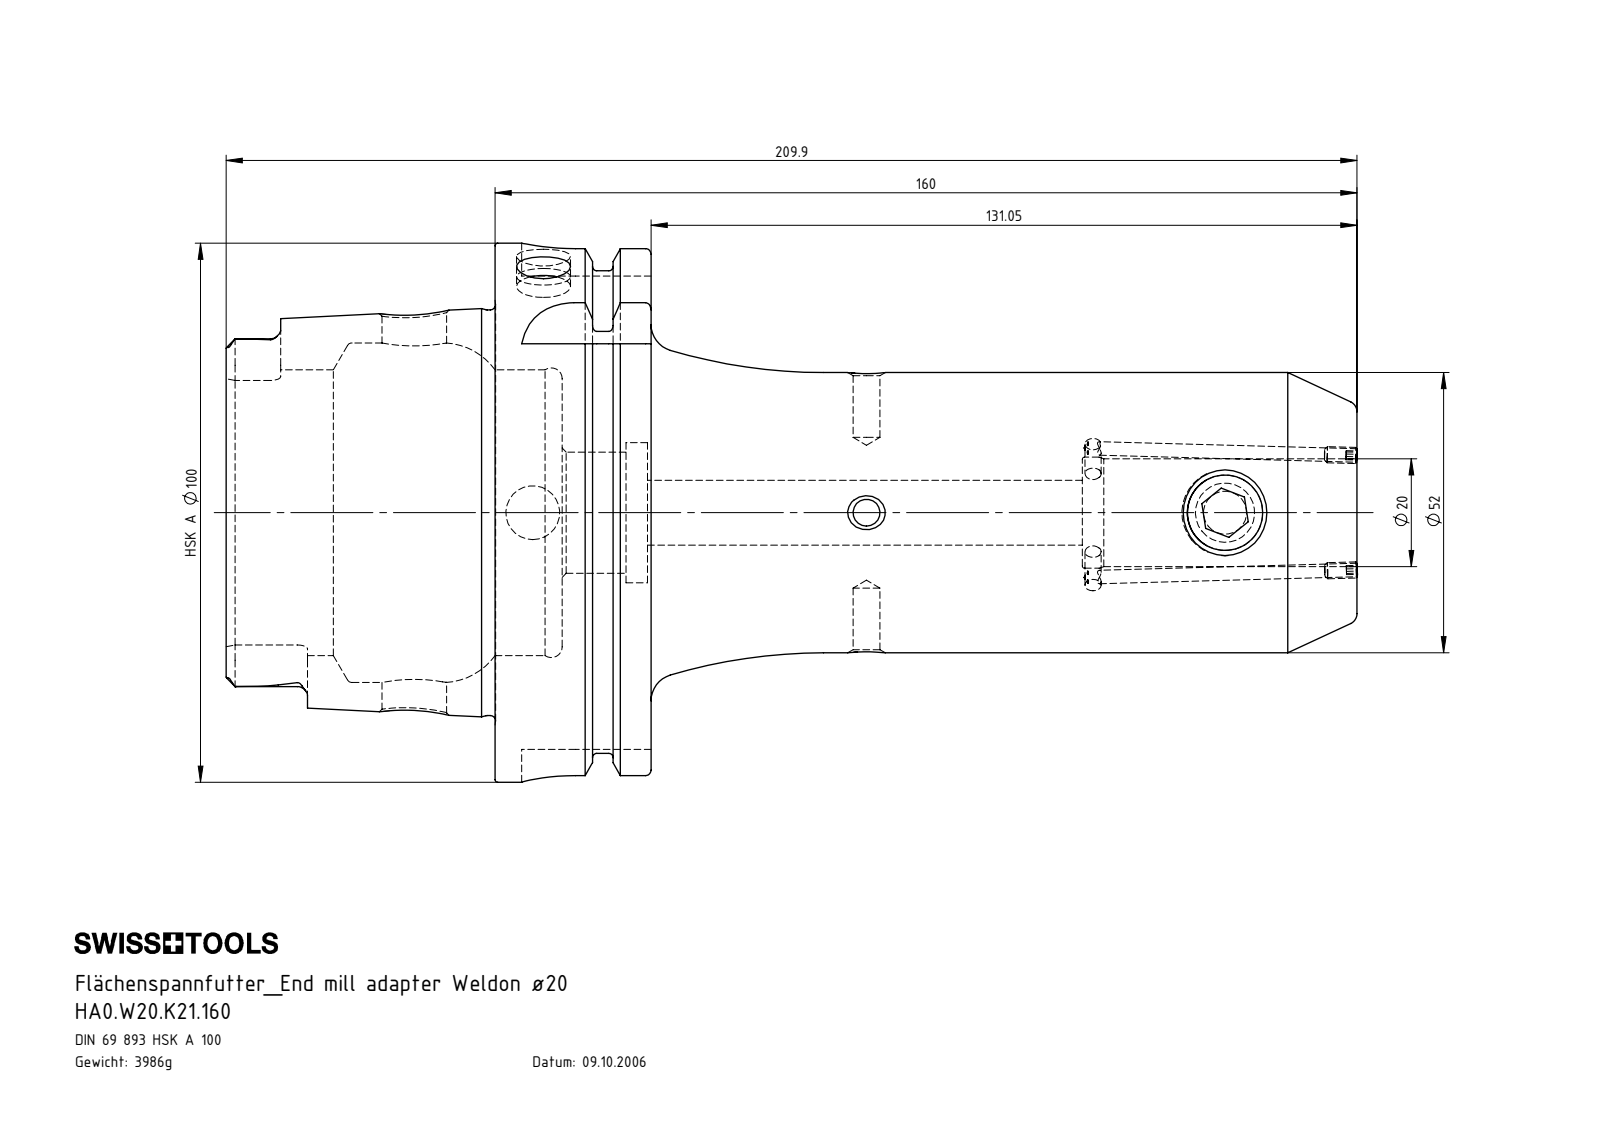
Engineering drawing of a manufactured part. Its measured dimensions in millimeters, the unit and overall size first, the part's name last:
Units: millimetres
Overall size (bounding box): 209.98 × 100 × 100
Round holes (diameter × count): ⌀10 ×3, ⌀2.5 ×2, ⌀5 ×2, ⌀12 ×2, ⌀3 ×1, ⌀14 ×1, ⌀20 ×1, ⌀20.6 ×1, ⌀22.5 ×1, ⌀26 ×1, ⌀53 ×1, ⌀63 ×1
Round bosses / shafts (diameter × count): ⌀3 ×2, ⌀100 ×1, ⌀91.95 ×1, ⌀75.26 ×1, ⌀52 ×1, ⌀16 ×1
Partial cylindrical surfaces — rounded edges, fillets, slot ends (radius × count): R1.9 ×6, R4.88 ×4, R10 ×4
Main face-to-face distances: 28.95, 16.5, 12.45, 49.9, 62.35, 78.85, 209.9, 160, 147.55, 131.05
Hole centre spacings: 61.95, 66.55, 83.95, 128.5
Volume: 507 733 mm³ · Surface area: 79 432 mm²
Bodies: 4 solids, 273 faces (71 planar, 82 cylindrical, 120 other)
Part name (STEP PRODUCT): HA0.W20.K21.160; HA0-W20.K21.160_D_Fertigbearbeitung; ERU-CJ2.001.006_Default; W20-ER1.001.016_Default
STEP written by: SolidWorks 2009 (CONFIG_CONTROL_DESIGN)
